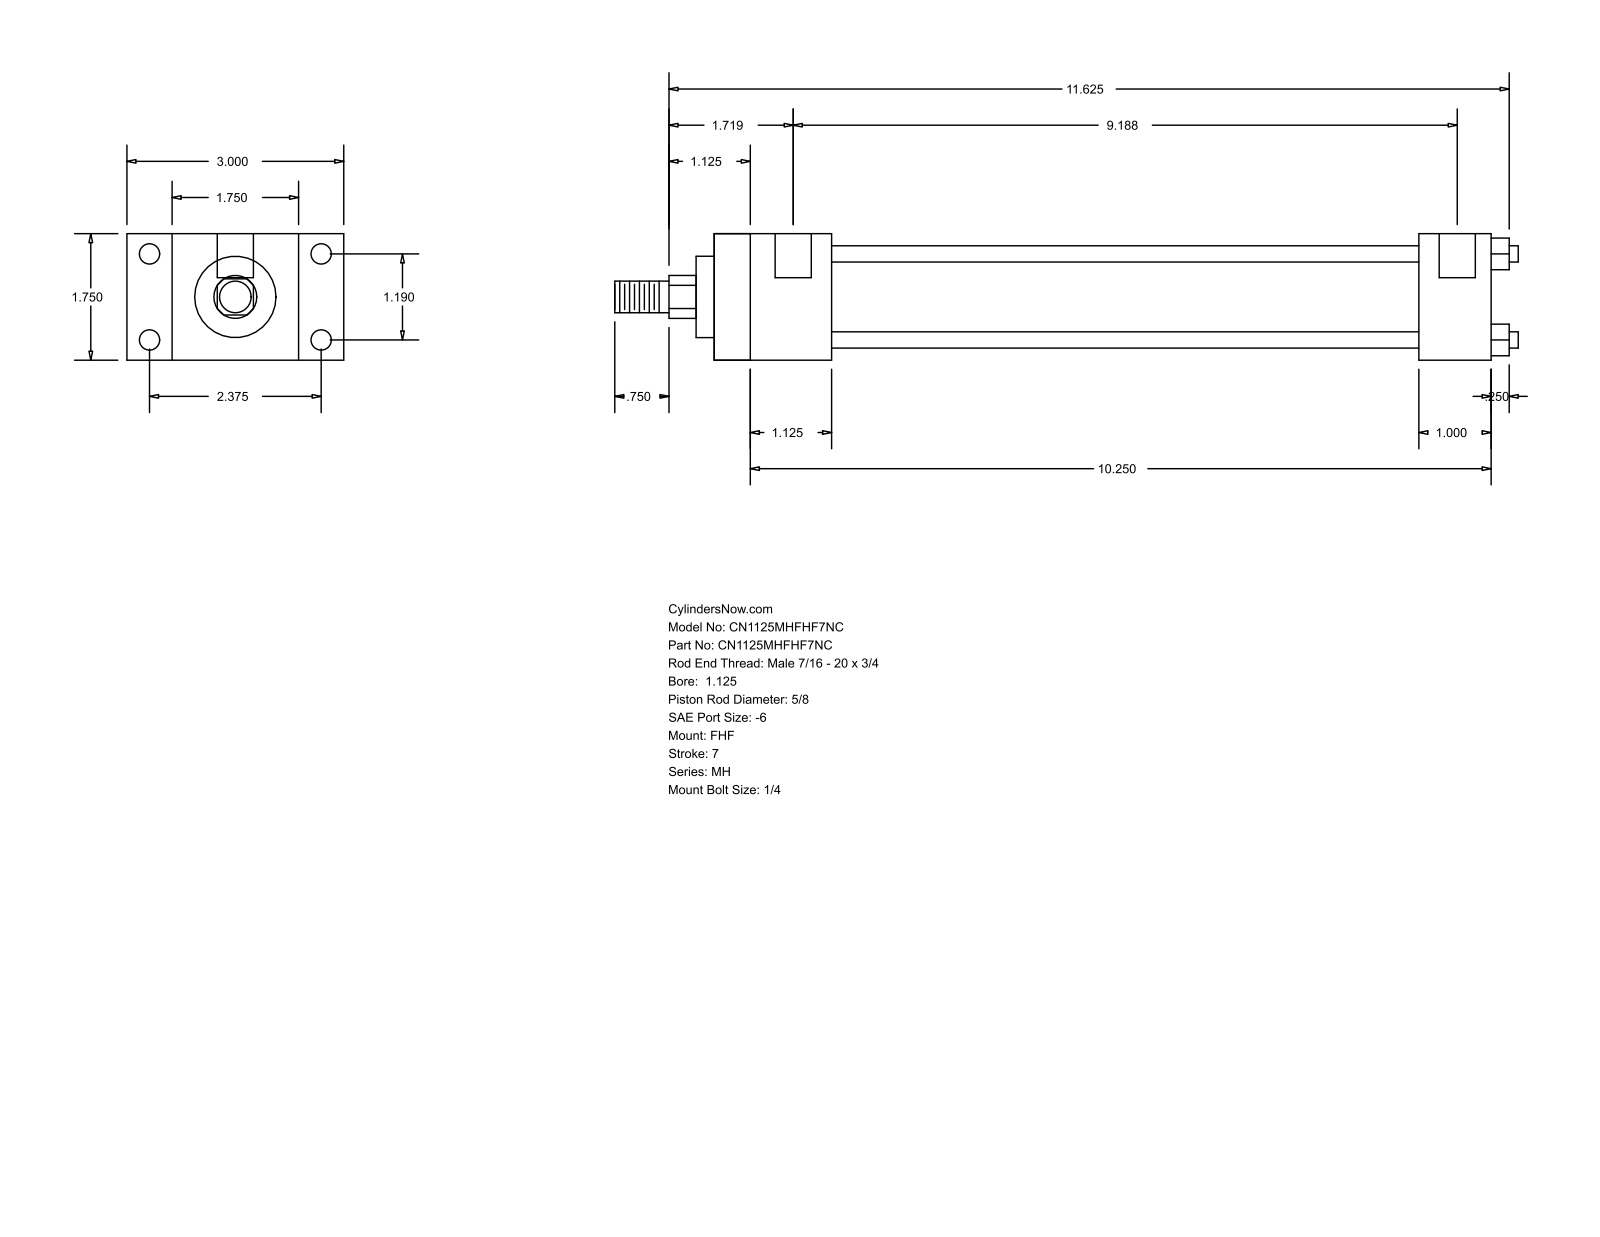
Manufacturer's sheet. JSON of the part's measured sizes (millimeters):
{"part_name": "MH_FHF__0112_0.625", "step_written_by": "GSSL Pune (CONFIG_CONTROL_DESIGN)", "units": "millimeters", "bodies": {"solids": 0, "faces": 88, "planar": 60, "cylindrical": 28, "other": 0}, "overall_size": [317.5, 76.2, 44.45], "round_holes": [[5.56, 4], [7.14, 4], [12.7, 2]], "round_bosses_or_shafts": [[5.71, 4], [34.92, 1], [28.57, 1], [15.88, 1], [11.11, 1]], "partial_cylinders_radius": [[7.54, 1]], "face_to_face_distances": [44.46, 15.87, 60.33, 41.27, 76.2, 273.05, 231.78, 247.64, 206.37, 25.41], "hole_center_spacings": [30.22, 60.32, 67.47, 230.19, 3.17, 233.36]}
